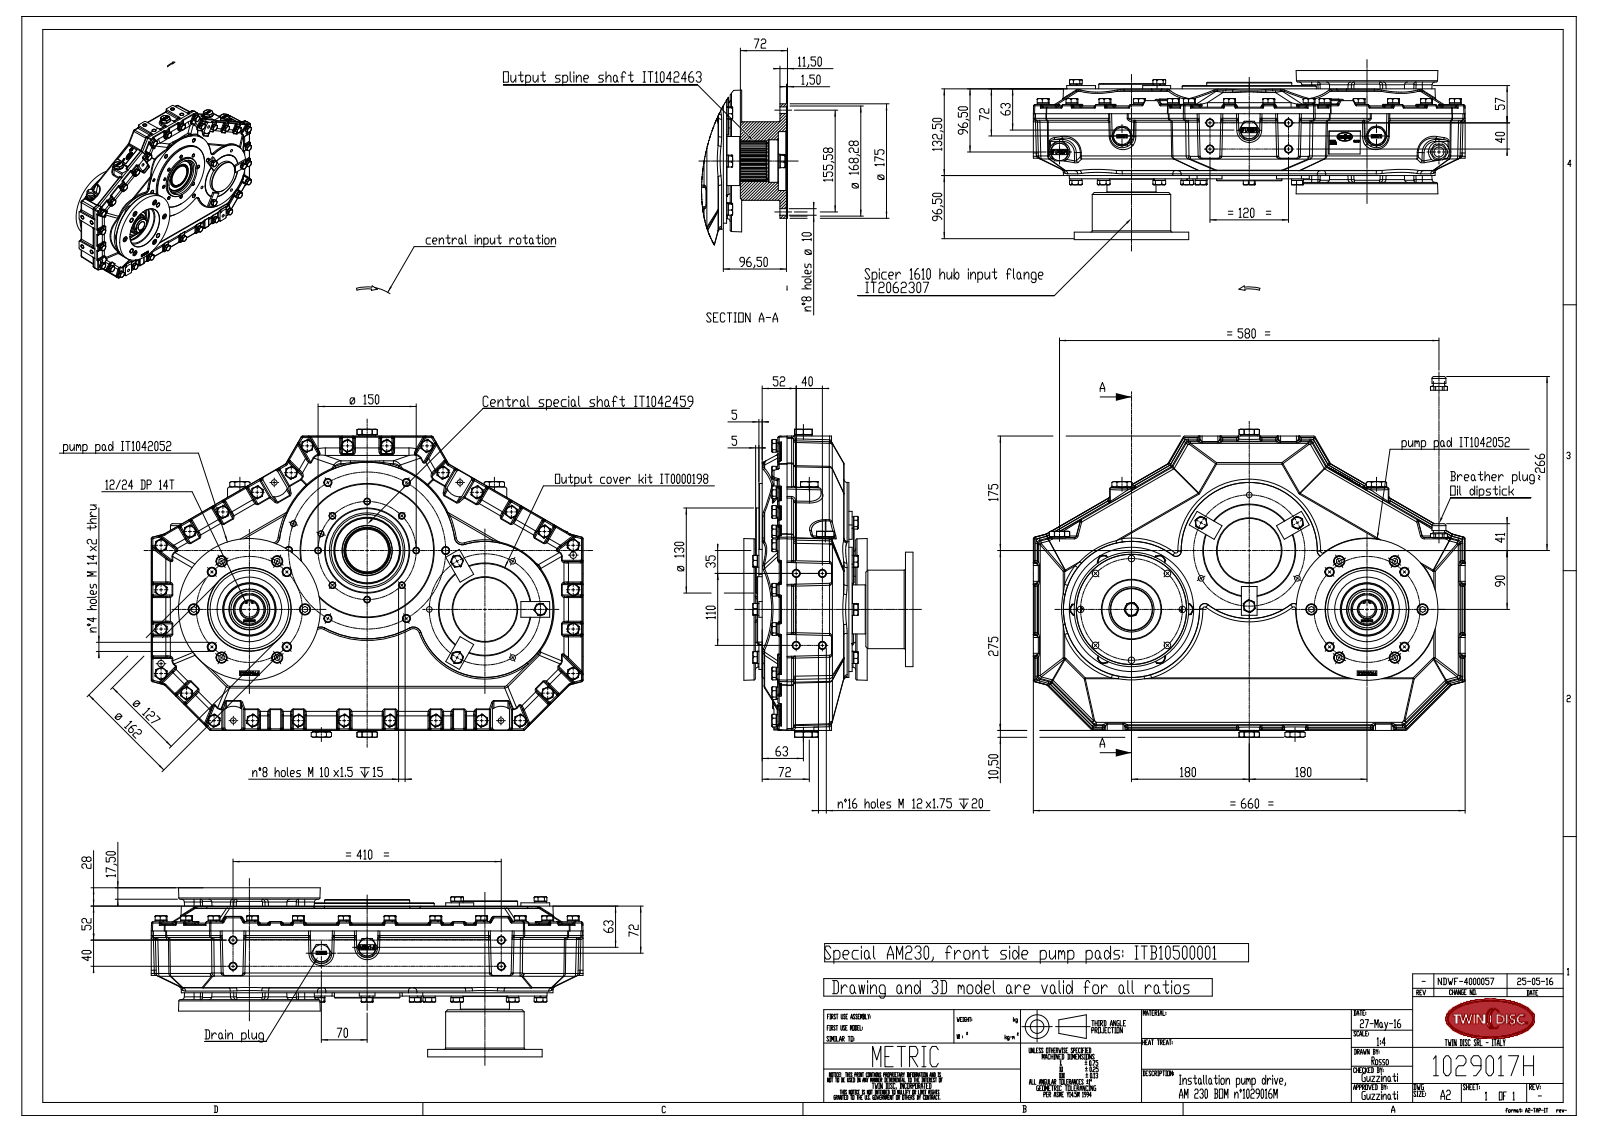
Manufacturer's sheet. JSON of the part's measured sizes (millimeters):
{"part_name": "IT2021216_rev03-installation; IT2062307_rev02-installation; IT1054022_rev00-installation; ITB00500000_rev00-installation (+8 more)", "step_written_by": "SolidWorks 2007 (AUTOMOTIVE_DESIGN)", "units": "millimeters", "bodies": {"solids": 42, "faces": 7848, "planar": 2919, "cylindrical": 2465, "other": 2464}, "overall_size": [690.04, 660, 258.5], "volume_mm3": 4858000, "surface_area_mm2": 2092000, "round_holes": [[10.2, 57], [10.5, 36], [8.5, 30], [12, 22], [10, 18], [11, 12], [17, 6], [14, 4], [18.5, 3], [21, 3], [80, 3], [2, 2]], "round_bosses_or_shafts": [[10, 45], [16.2, 39], [18.1, 38], [16, 6], [82, 3], [27, 3], [25.95, 3], [100, 2]], "partial_cylinders_radius": [[2, 201], [3, 103], [2.5, 78], [5, 74], [0.45, 58], [4.5, 24], [13, 19], [1.5, 14]], "face_to_face_distances": [132.5, 125, 28, 5, 23, 122, 160.5, 31, 77, 148], "hole_center_spacings": [85, 120, 147.22, 40, 75, 207.84, 409.18, 57.4]}
